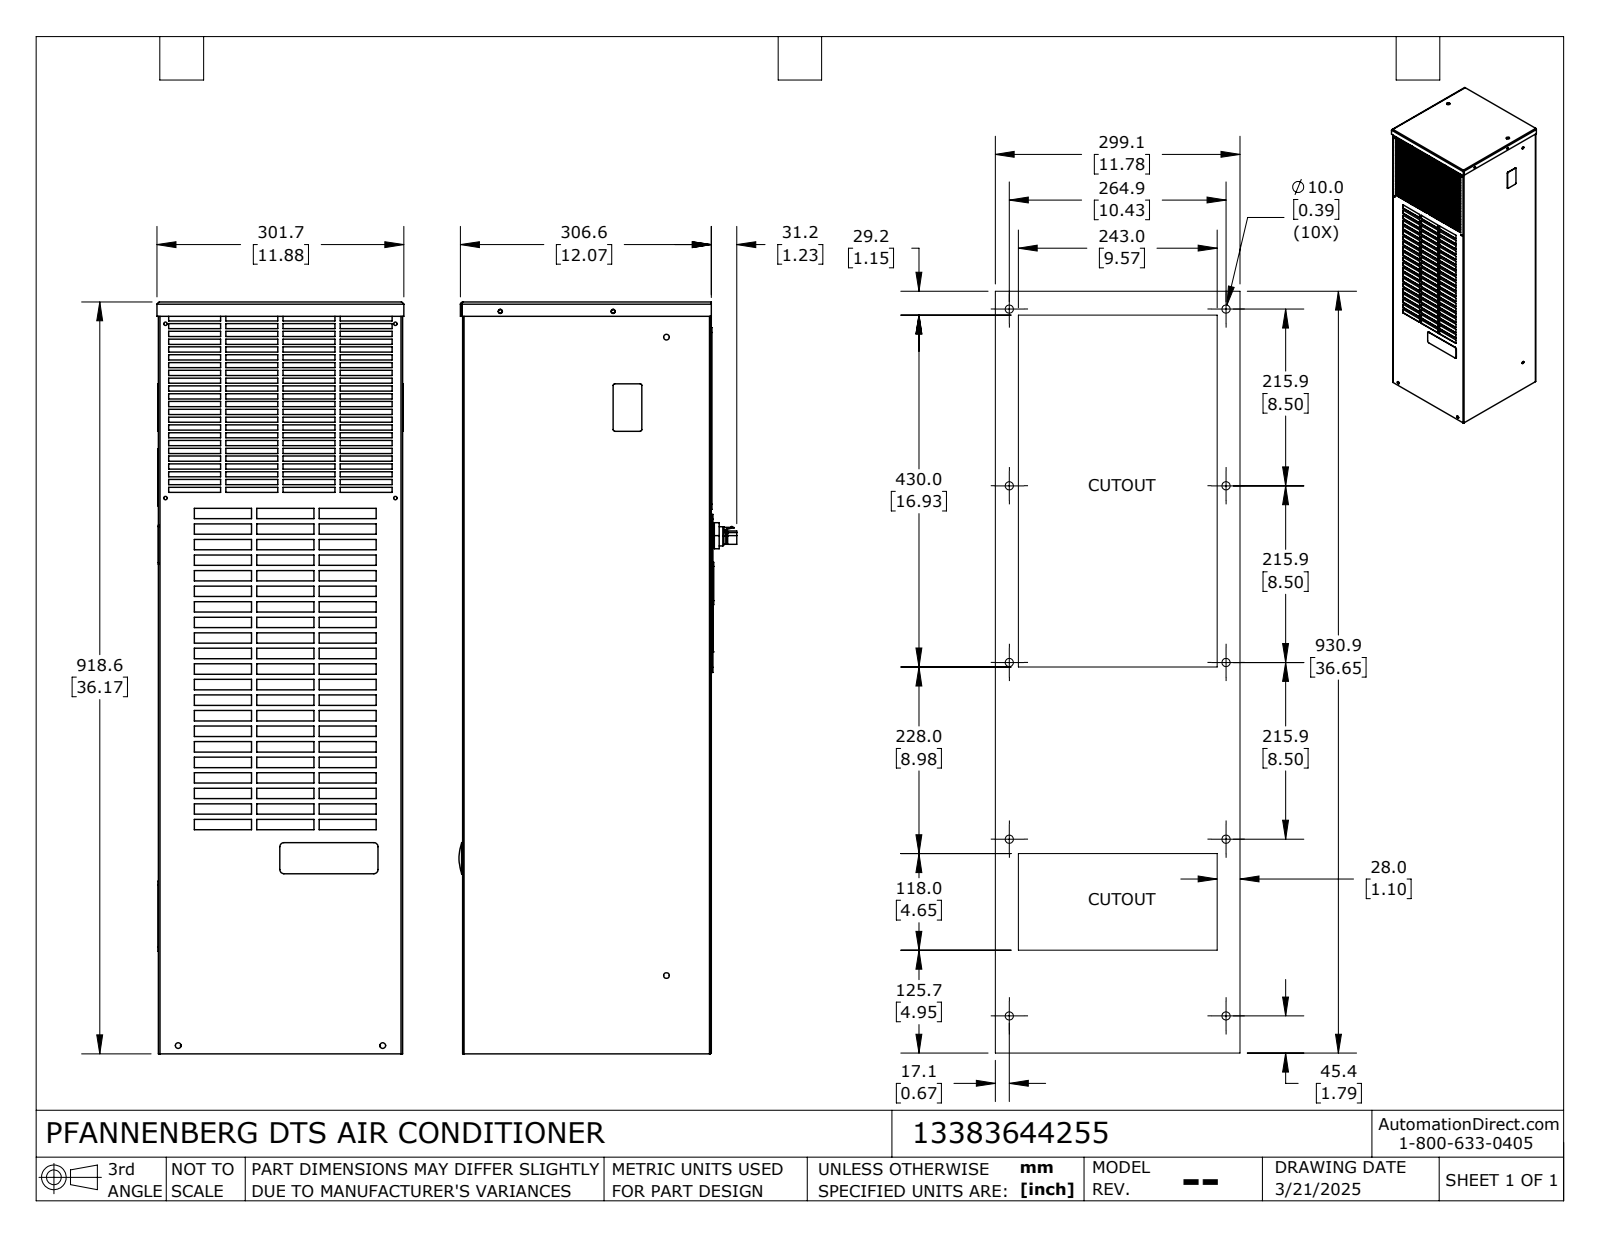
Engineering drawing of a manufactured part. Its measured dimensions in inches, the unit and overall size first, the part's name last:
Units: inches
Overall size (bounding box): 36.165 × 13.373 × 11.878
Round holes (diameter × count): ⌀0.165 ×29, ⌀0.189 ×10, ⌀0.276 ×6, ⌀0.169 ×5, ⌀0.209 ×5, ⌀0.122 ×4, ⌀0.161 ×4, ⌀0.17 ×2, ⌀0.203 ×2, ⌀0.394 ×2, ⌀0.945 ×2, ⌀0.315 ×1
Round bosses / shafts (diameter × count): ⌀0.079 ×4, ⌀0.866 ×2, ⌀1.378 ×1, ⌀0.906 ×1
Partial cylindrical surfaces — rounded edges, fillets, slot ends (radius × count): R0.125 ×112, R0.031 ×13, R0.079 ×12, R0.197 ×12, R0.087 ×10, R0.236 ×10, R0.078 ×4, R0.125 ×4
Main face-to-face distances: 11.812, 11.752, 0.045, 0.056, 11.843, 0.031, 0.083, 11.895, 11.926, 0.076
Hole centre spacings: 0.294, 0.244, 1.496, 0.231, 0.254, 0.454, 0.655, 0.655
Volume: 4 949 in³ · Surface area: 3 717 in²
Bodies: 1 solid, 1716 faces (1188 planar, 475 cylindrical, 53 other)
Part name (STEP PRODUCT): 13383644255_Default
STEP written by: SolidWorks 2024 (CONFIG_CONTROL_DESIGN)
